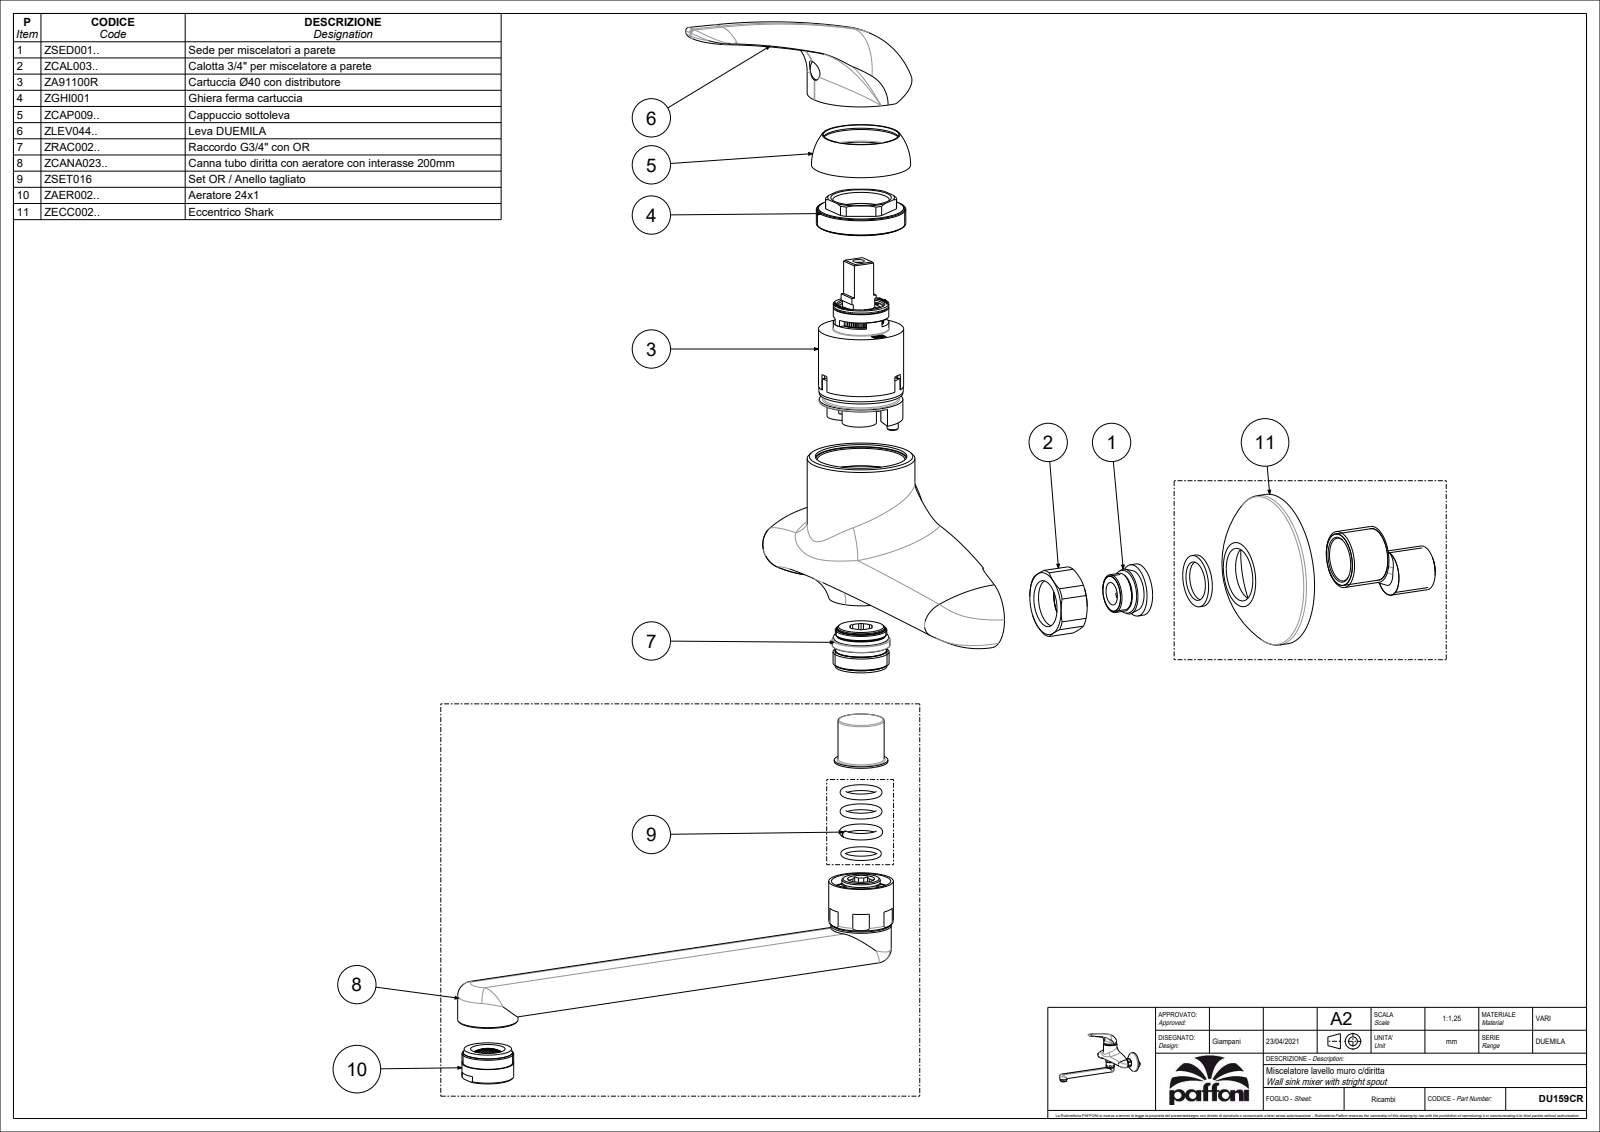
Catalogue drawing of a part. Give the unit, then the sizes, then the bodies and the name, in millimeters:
Units: millimetres
Overall size (bounding box): 273.5 × 220 × 163.42
Round holes (diameter × count): ⌀9.2 ×1, ⌀14.9 ×1, ⌀16.5 ×1, ⌀17.3 ×1, ⌀18.2 ×1, ⌀18.5 ×1, ⌀20 ×1, ⌀21 ×1, ⌀21.2 ×1, ⌀23 ×1, ⌀26 ×1, ⌀27 ×1
Round bosses / shafts (diameter × count): ⌀70 ×2, ⌀28 ×2, ⌀24 ×2, ⌀50 ×1, ⌀30 ×1, ⌀26.8 ×1, ⌀26 ×1, ⌀21 ×1
Partial cylindrical surfaces — rounded edges, fillets, slot ends (radius × count): R1.5 ×2, R7 ×2, R8 ×2, R15 ×2, R15.5 ×2, R20.5 ×2, R24 ×2, R24.5 ×2
Main face-to-face distances: 1, 15, 34.5, 14, 16, 35.5, 0.5, 1.5, 106.7, 121.7
Hole centre spacings: 200
Volume: 505 706 mm³ · Surface area: 105 441 mm²
Bodies: 2 solids, 277 faces (72 planar, 82 cylindrical, 123 other)
Part name (STEP PRODUCT): DU159CR
STEP written by: CREO PARAMETRIC BY PTC INC, 2020044 (CONFIG_CONTROL_DESIGN)
